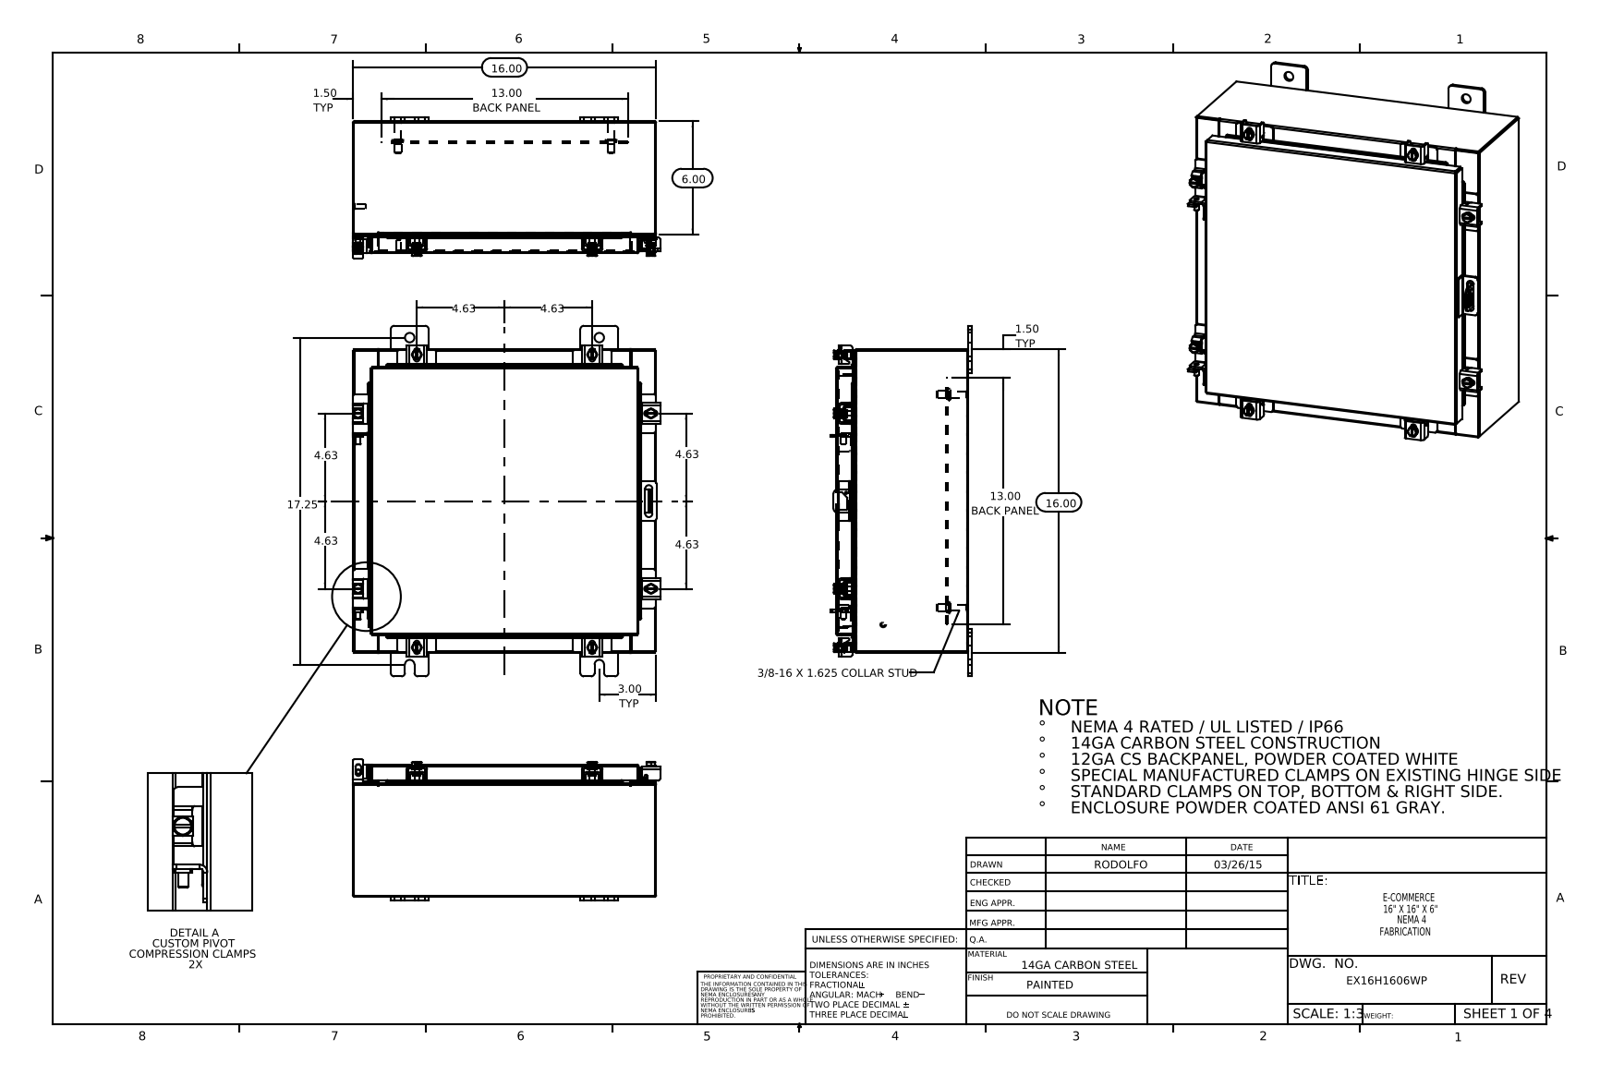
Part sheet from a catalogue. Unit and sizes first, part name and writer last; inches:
Units: inches
Overall size (bounding box): 18.5 × 16.211 × 7.453
Round holes (diameter × count): ⌀0.213 ×8, ⌀0.26 ×8, ⌀0.5 ×8, ⌀0.125 ×1, ⌀0.25 ×1
Round bosses / shafts (diameter × count): ⌀0.5 ×8, ⌀0.25 ×8, ⌀0.399 ×6, ⌀0.625 ×4, ⌀0.375 ×4, ⌀0.33 ×4, ⌀0.315 ×2, ⌀0.236 ×2
Partial cylindrical surfaces — rounded edges, fillets, slot ends (radius × count): R0.06 ×34, R0.19 ×24, R0.013 ×22, R0.088 ×22, R0.1 ×16, R0.09 ×14, R0.12 ×14, R0.141 ×12
Main face-to-face distances: 0.075, 6.9, 15.925, 6.975, 6.826, 15.85, 16, 1, 1.075, 5.826
Hole centre spacings: 13.388, 10.463, 2.326, 12.734, 15.451, 16.831, 16.832, 17.467
Volume: 101.4 in³ · Surface area: 2 548 in²
Bodies: 59 solids, 1468 faces (791 planar, 549 cylindrical, 128 other)
Part name (STEP PRODUCT): EX16H1606WP Special Clamp; Special Clamp Assembly; 22104005_DEFAULT_RTP30; EX16H1606WP Mounting Studs (+8 more)
STEP written by: SolidWorks 2014 (CONFIG_CONTROL_DESIGN)
